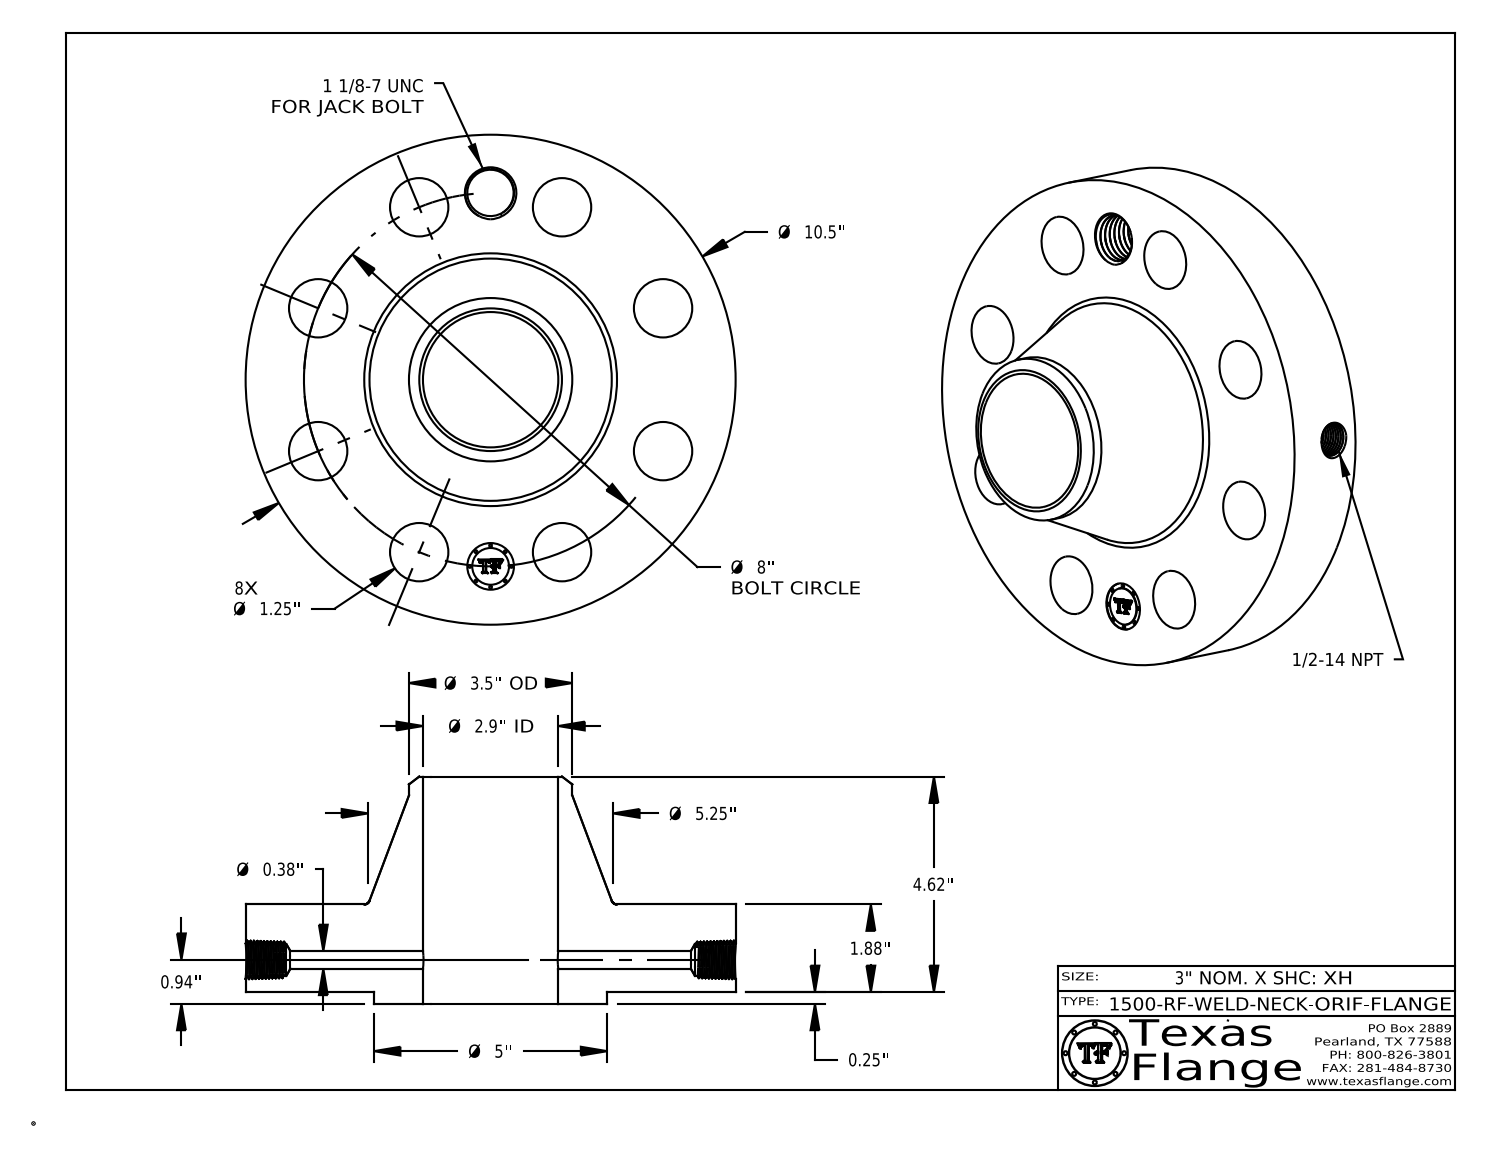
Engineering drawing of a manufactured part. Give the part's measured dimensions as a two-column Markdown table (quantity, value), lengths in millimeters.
| quantity | value |
| --- | --- |
| part name | 1500-RF-WELD-NECK |
| STEP written by | CATIA V5 STEP AP214 (AUTOMOTIVE_DESIGN) |
| units | millimeters |
| bodies | 1 solid, 760 faces (369 planar, 90 cylindrical, 301 other) |
| overall size | 266.7 × 266.7 × 123.7 |
| volume | 2 512 000 mm³ |
| surface area | 229 200 mm² |
| round holes (diameter × count) | 31.8 × 8, 9.5 × 1, 17.1 × 1, 25 × 1, 25.4 × 1, 73.7 × 1 |
| round bosses / shafts (diameter × count) | 1.5 × 8, 266.7 × 1, 127 × 1, 88.9 × 1, 20 × 1 |
| main face-to-face distances | 47.8, 6.4, 54.1, 123.7, 117.3, 69.6, 53.7, 47.4, 0.4, 70 |
| hole center spacings | 101.6, 143.7, 187.7, 39.6, 77.7, 77.8, 112.9, 169 |
